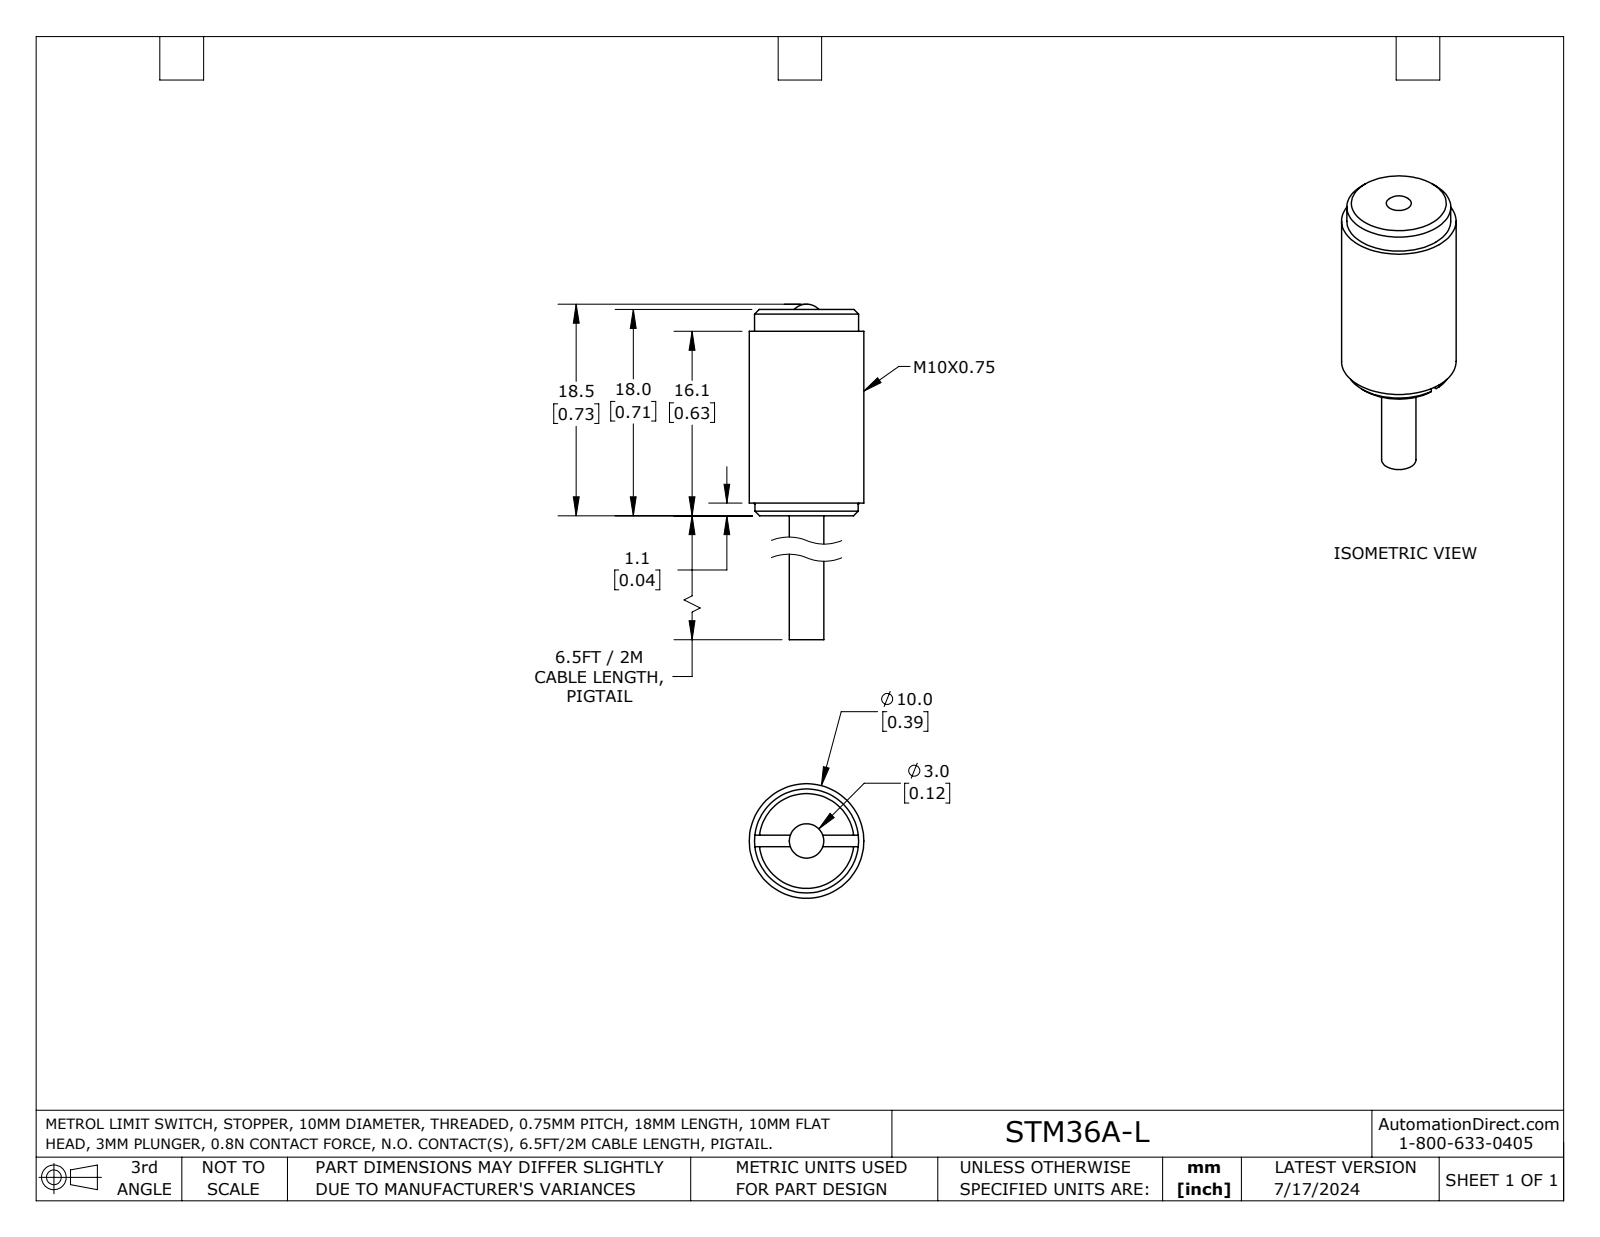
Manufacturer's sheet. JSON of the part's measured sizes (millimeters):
{"part_name": "STM36A-L", "step_written_by": "SolidWorks 2023 (AUTOMOTIVE_DESIGN)", "units": "millimeters", "bodies": {"solids": 1, "faces": 20, "planar": 12, "cylindrical": 4, "other": 4}, "overall_size": [27.9, 10, 10], "volume_mm3": 1500, "surface_area_mm2": 815, "round_bosses_or_shafts": [[10, 1], [9.1, 1], [3.5, 1]], "face_to_face_distances": [18, 16.1, 1.9, 1.1, 15, 16.9, 1, 9.4, 10.5, 25.5]}
